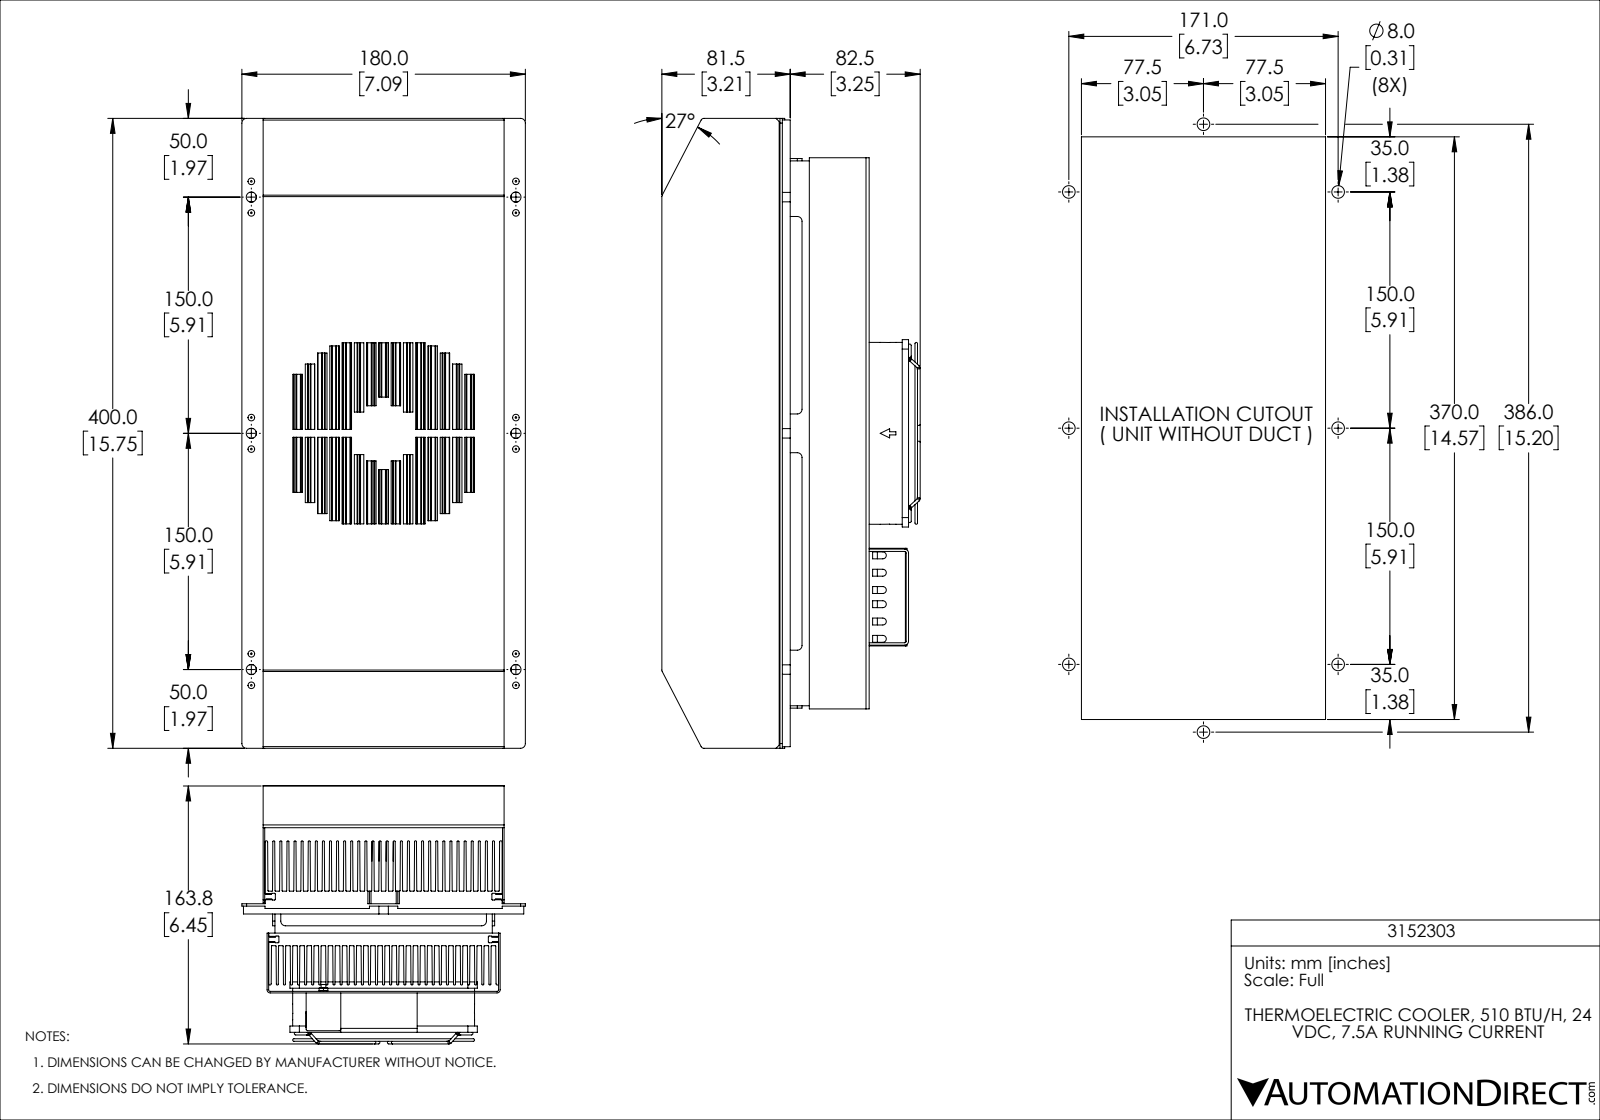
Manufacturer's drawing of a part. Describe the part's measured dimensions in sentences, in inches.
The part is named "3152303_UNI". Its 3-D file was written by "SolidWorks 2019 (AUTOMOTIVE_DESIGN)". It is 5 solids with 1828 faces: 1207 planar, 523 cylindrical and 98 other. Overall it measures 15.748 by 7.087 by 6.458 inches. Its volume is 188.3 cubic inches and its surface area 3 155 square inches. Round holes: 14 of diameter 0.236, 12 of diameter 0.165, 8 of diameter 0.177, 8 of diameter 0.256, 8 of diameter 0.394, 4 of diameter 0.126, 4 of diameter 0.169, 4 of diameter 0.244, 1 of diameter 4.39. Round bosses or shafts: 12 of diameter 0.071, 4 of diameter 0.236, 4 of diameter 0.118, 4 of diameter 0.098, 1 of diameter 4.547, 1 of diameter 2.441. Partial cylindrical surfaces (rounded edges, fillets, slot ends): 132 of radius 0.012, 63 of radius 0.024, 44 of radius 0.02, 31 of radius 0.039, 10 of radius 0.118, 6 of radius 0.079, 6 of radius 0.087, 4 of radius 0.031. The main face-to-face distances are 0.177, 0.354, 0.531, 0.709, 0.886, 1.063, 1.24, 1.417, 1.594, 1.772. The hole center spacings are 5.906, 0.278, 0.289, 0.447, 0.568, 0.686, 1.22, 0.35.
